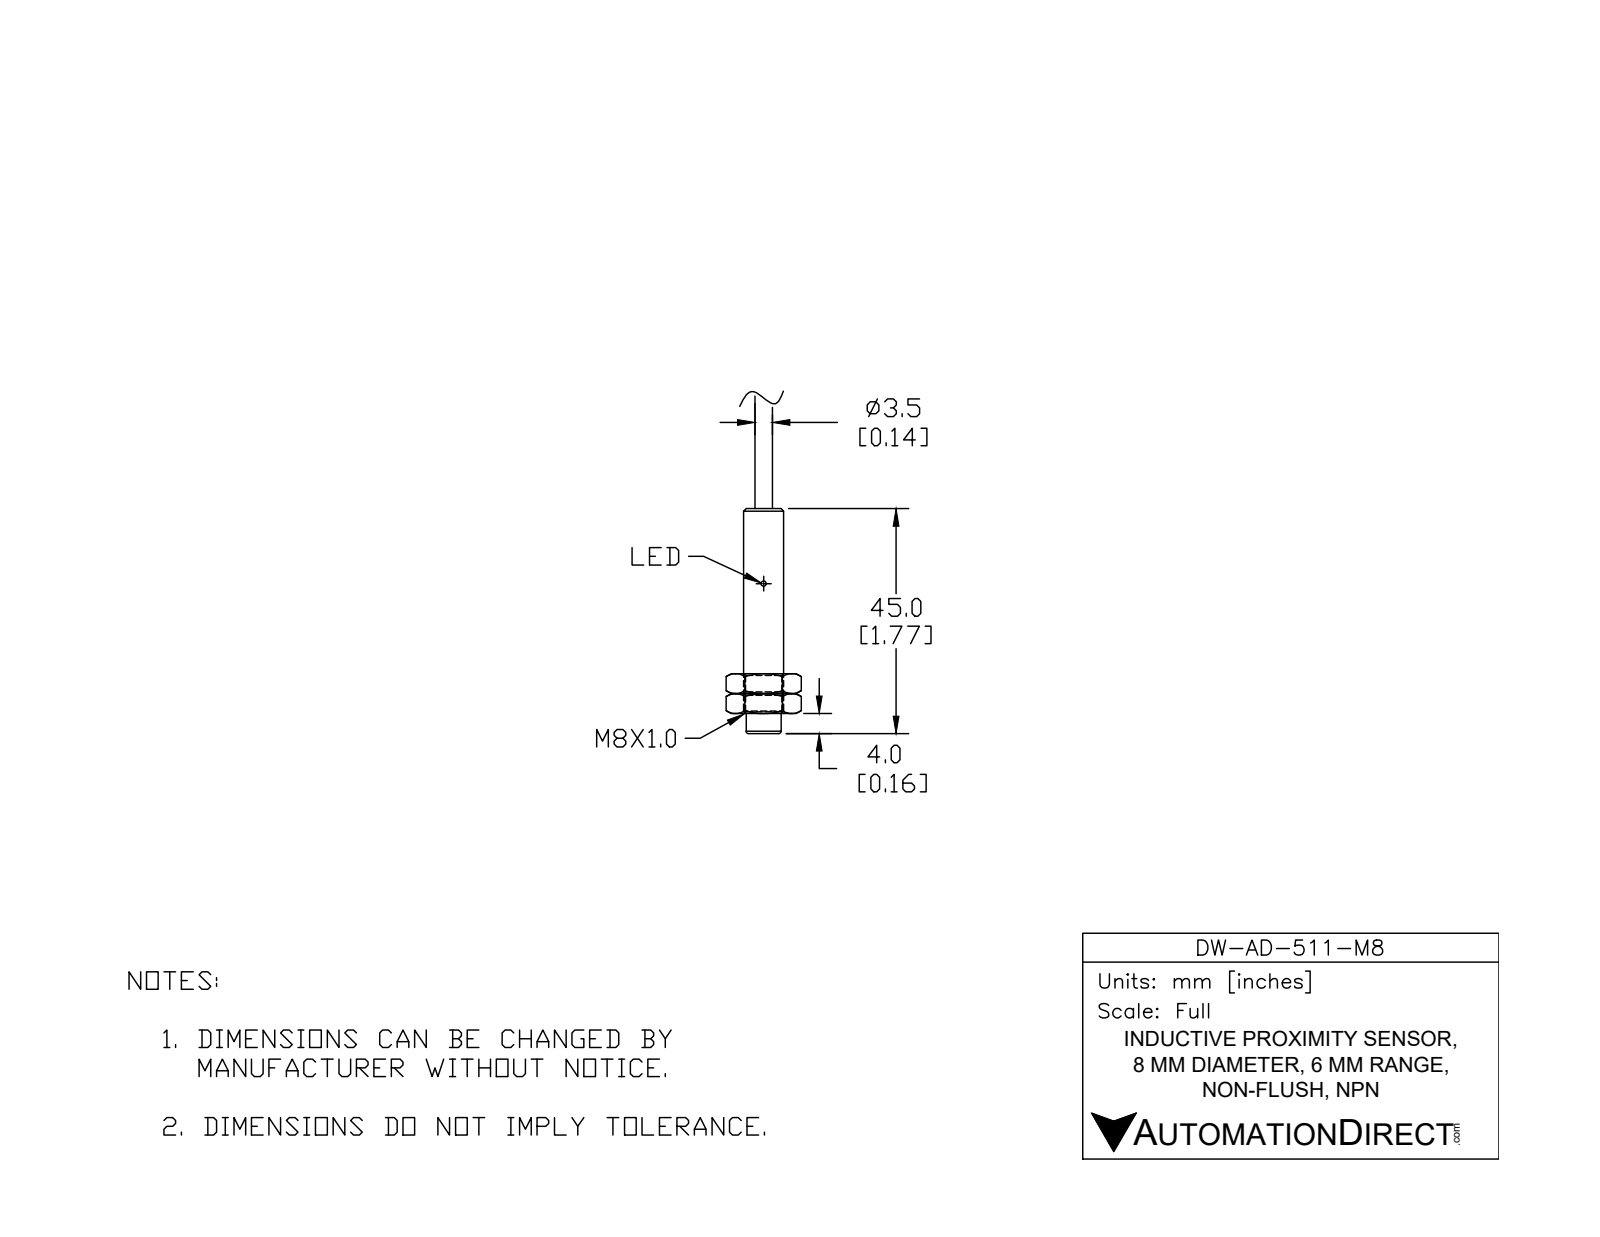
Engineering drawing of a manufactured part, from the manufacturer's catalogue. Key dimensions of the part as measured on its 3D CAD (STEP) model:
Part name (STEP PRODUCT): DW-AD-511-M8
STEP written by: SolidWorks 2017 (AUTOMOTIVE_DESIGN)
Units: inches
Bodies: 2 solids, 14 faces (6 planar, 4 cylindrical, 4 other)
Overall size (bounding box): 2.803 × 0.315 × 0.315
Volume: 0.166 in³ · Surface area: 2.617 in²
Round bosses / shafts (diameter × count): ⌀0.315 ×1, ⌀0.272 ×1, ⌀0.256 ×1, ⌀0.197 ×1
Main face-to-face distances: 0.165, 2.803, 2.638, 1.791, 1.626, 1.012, 1.772, 1.606, 0.02, 1.031
